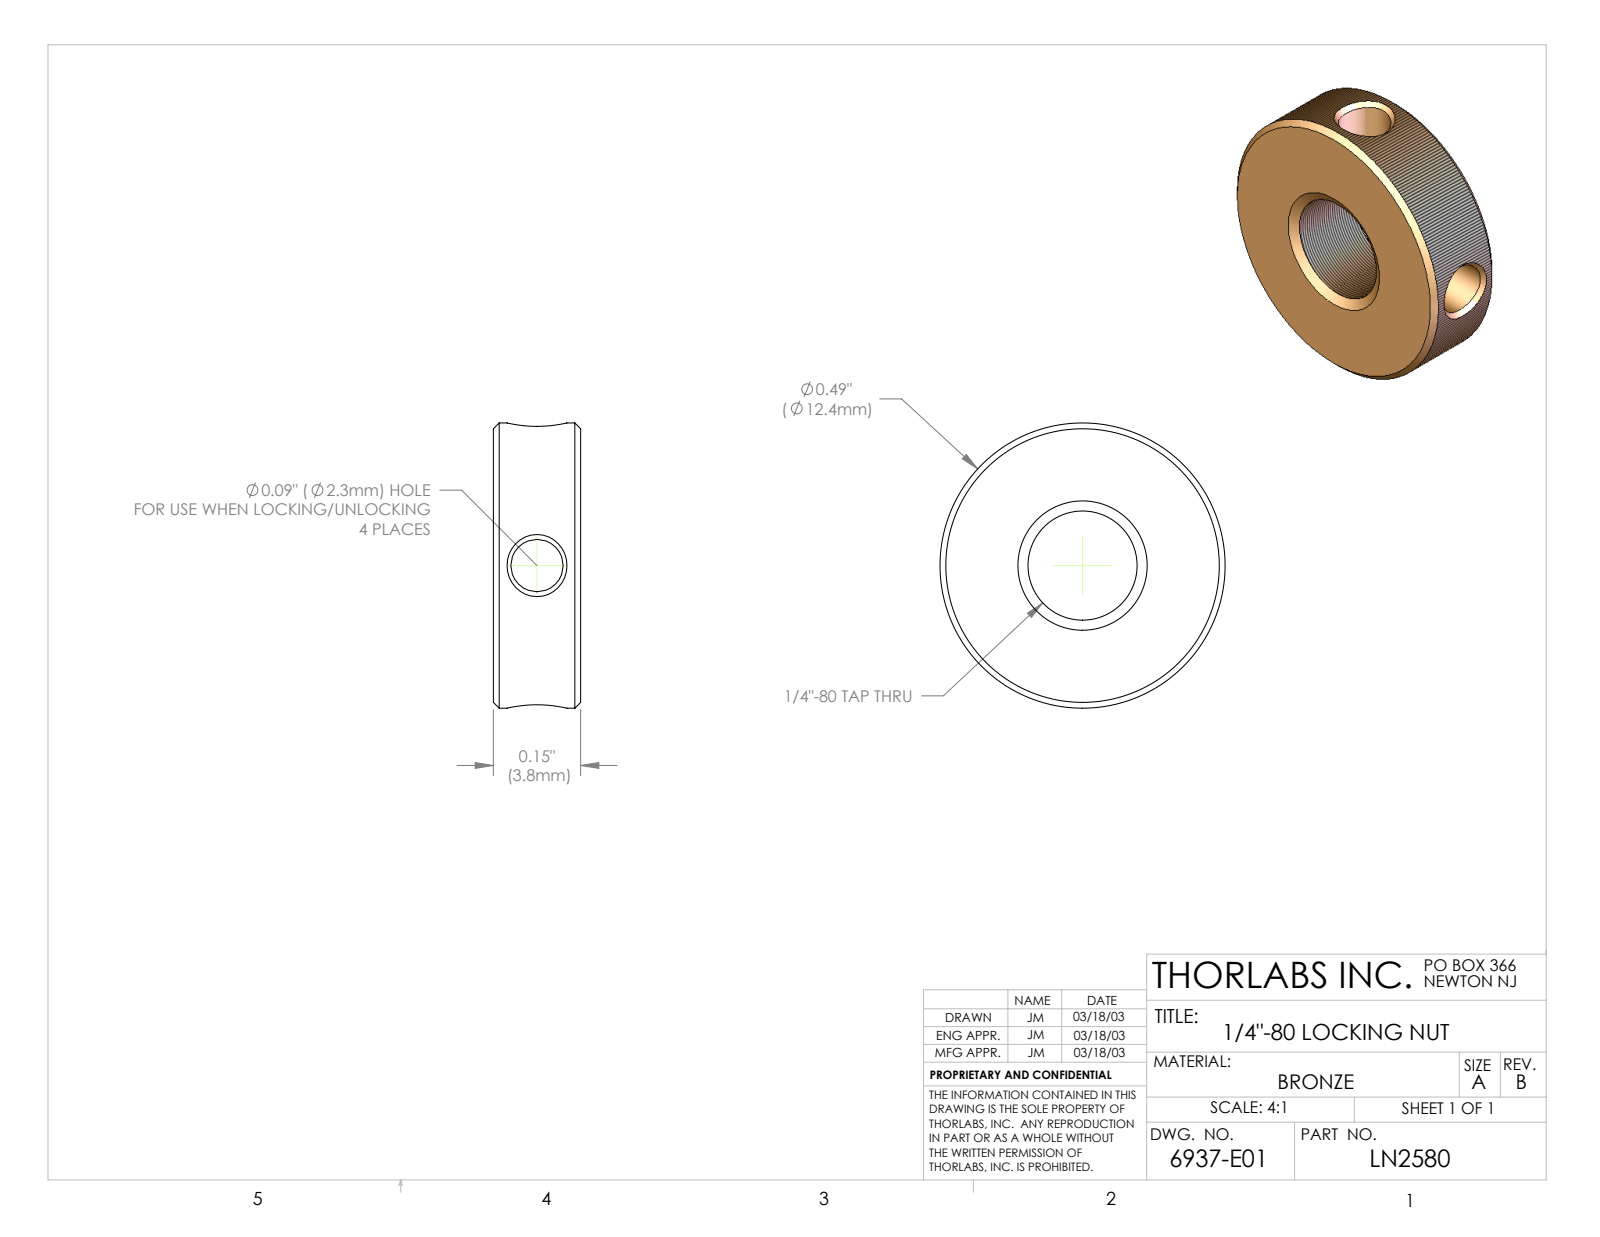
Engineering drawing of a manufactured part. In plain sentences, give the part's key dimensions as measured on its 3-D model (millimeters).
The part is named "6937-E0W". Its 3-D file was written by "SolidWorks 2016 (AUTOMOTIVE_DESIGN)". It is 1 solid with 34 faces: 6 planar, 12 cylindrical and 16 other. Overall it measures 12.4 by 12.4 by 3.8 millimeters. Its volume is 290 cubic millimeters and its surface area 454 square millimeters. Round holes: 2 of diameter 2.3, 1 of diameter 6.4. Round bosses or shafts: 1 of diameter 12.4. The main face-to-face distances are 3.8, 7.4.
